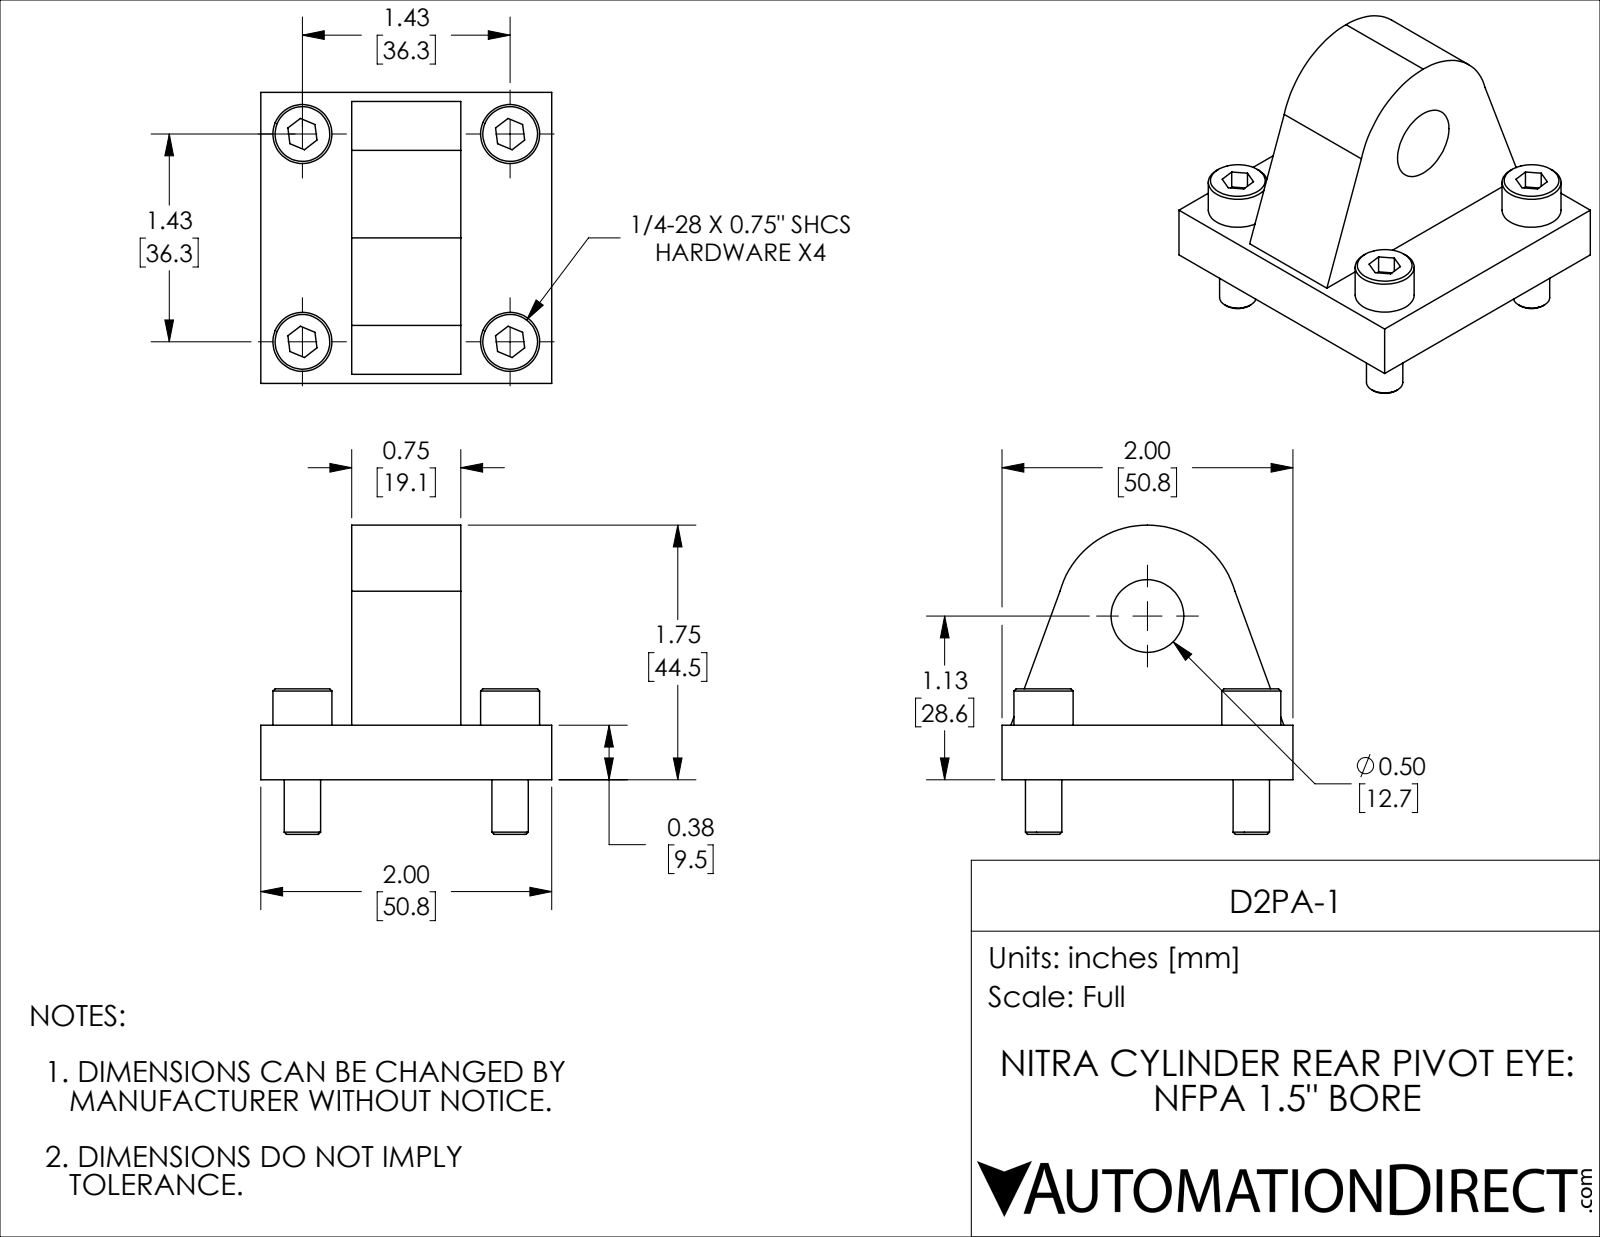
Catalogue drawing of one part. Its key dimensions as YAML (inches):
part_name: "D2PA-1"
step_written_by: "SolidWorks 2019 (CONFIG_CONTROL_DESIGN)"
units: inches
bodies: {solids: 5, faces: 94, planar: 50, cylindrical: 28, other: 16}
overall_size: [2.125, 2, 2]
volume: 2.885
surface_area: 22.45
round_holes:
  - {diameter: 0.281, count: 4}
  - {diameter: 0.5, count: 1}
round_bosses_or_shafts:
  - {diameter: 0.406, count: 4}
  - {diameter: 0.25, count: 4}
partial_cylinders:
  - {radius: 0.625, count: 1}
face_to_face_distances: [0.375, 0.75, 0.625, 1.375, 2, 0.25, 0.625, 1, 0.75, 0.375]
hole_center_spacings: [1.428, 2.02]
